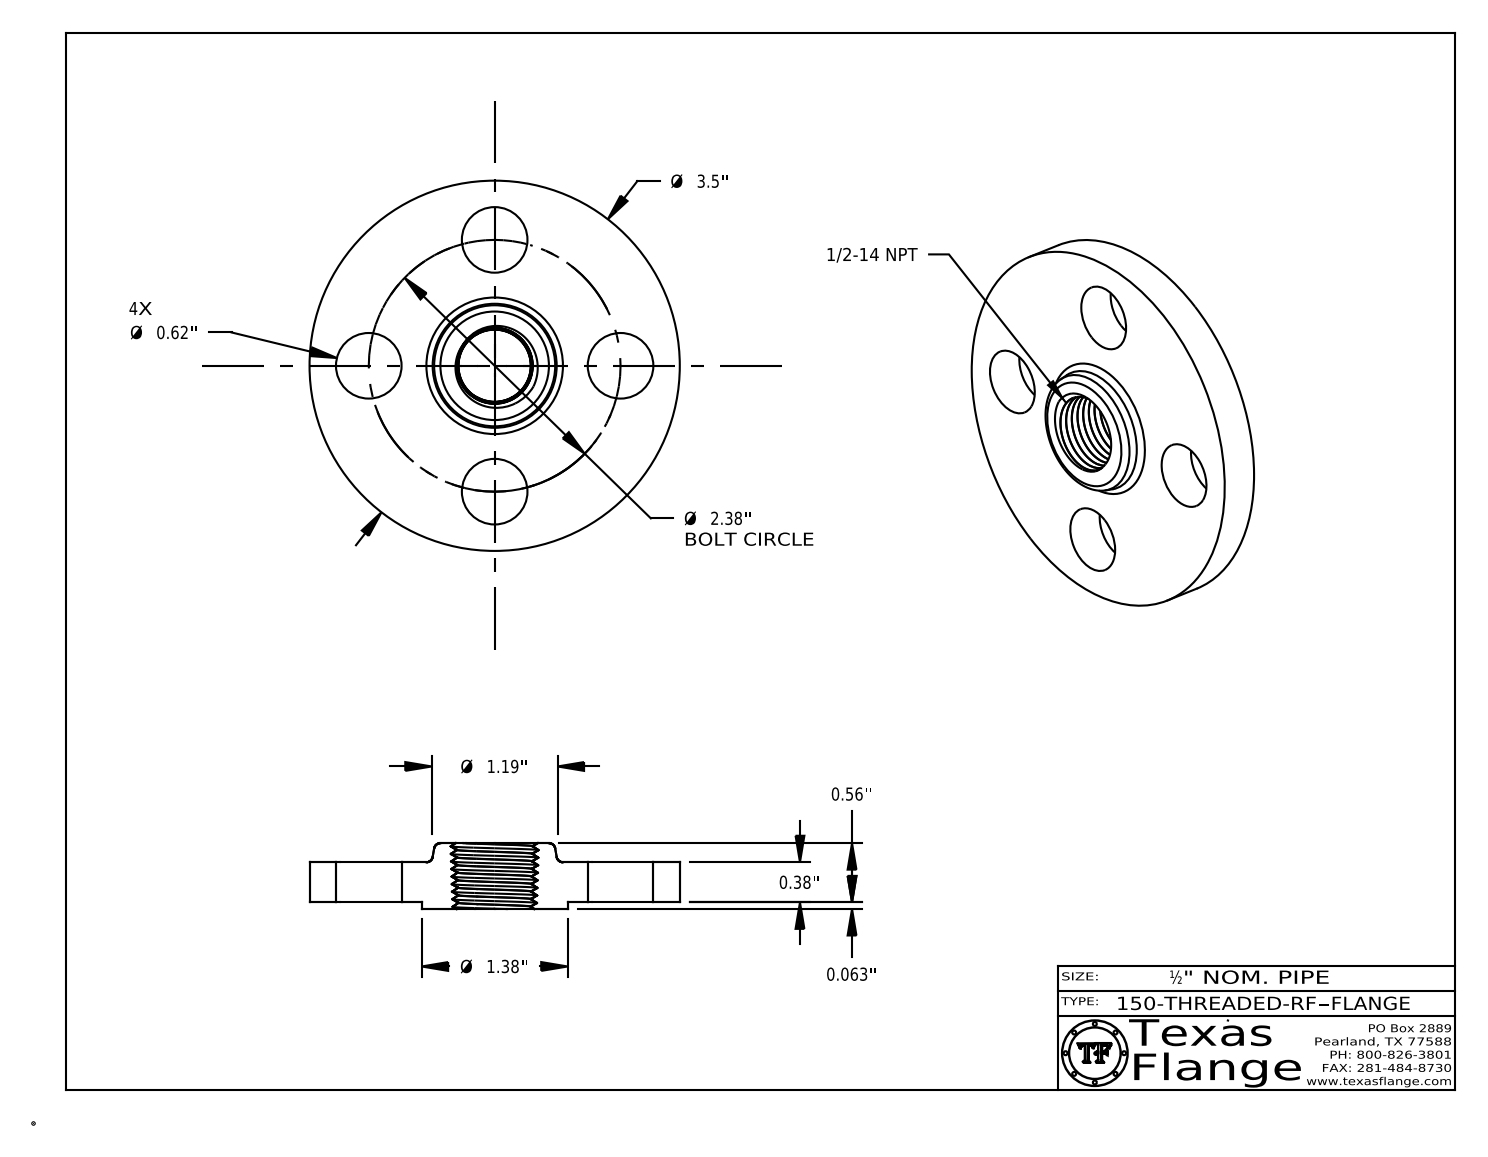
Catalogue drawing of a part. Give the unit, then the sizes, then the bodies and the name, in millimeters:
Units: millimetres
Overall size (bounding box): 88.9 × 88.9 × 15.8
Round holes (diameter × count): ⌀15.7 ×4, ⌀12.6 ×1
Round bosses / shafts (diameter × count): ⌀0.8 ×8, ⌀88.9 ×1, ⌀35.1 ×1, ⌀9.9 ×1
Main face-to-face distances: 9.7, 1.6, 11.3, 15.8, 14.2, 4.6, 10.9, 9.3, 0.4, 5
Hole centre spacings: 42.7, 23.1, 55.9, 60.5
Volume: 52 440 mm³ · Surface area: 17 170 mm²
Bodies: 1 solid, 504 faces (369 planar, 32 cylindrical, 103 other)
Part name (STEP PRODUCT): 150-THREADED-RF
STEP written by: CATIA V5 STEP AP214 (AUTOMOTIVE_DESIGN)
